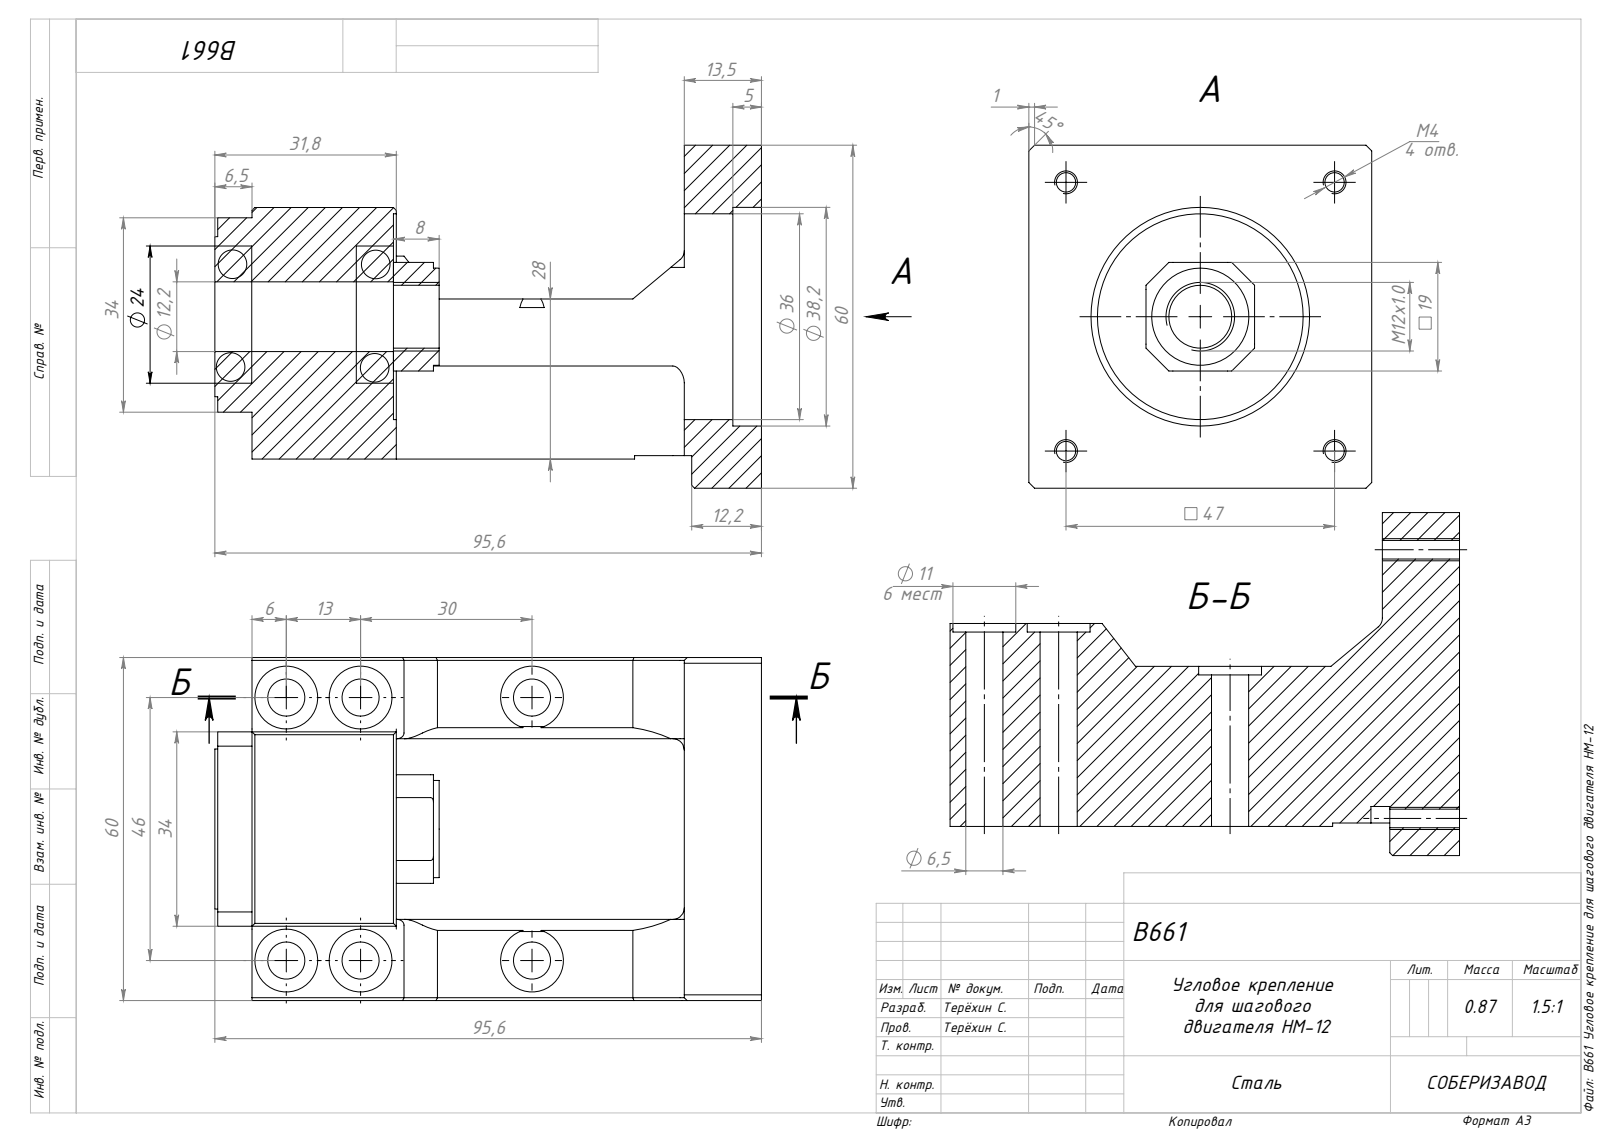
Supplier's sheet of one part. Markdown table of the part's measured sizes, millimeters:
| quantity | value |
| --- | --- |
| part name | B661 Угловое крепление для шагового двигателя HM-12; B661 Угловое крепление для шагового двигателя HM-12_00 |
| STEP written by | SolidWorks 2026 (CONFIG_CONTROL_DESIGN) |
| units | millimeters |
| bodies | 2 solids, 165 faces (89 planar, 74 cylindrical, 2 other) |
| overall size | 95.65 × 60 × 60 |
| volume | 130 514 mm³ |
| surface area | 34 753 mm² |
| round holes (diameter × count) | 11 × 7, 6.5 × 6, 3.4 × 4, 7.6 × 4, 12.2 × 1, 36 × 1, 38.25 × 1 |
| round bosses / shafts (diameter × count) | 28 × 1, 17 × 1 |
| partial cylindrical surfaces (radius × count) | 0.5 × 10, 1 × 4, 2 × 3, 2.15 × 2 |
| main face-to-face distances | 60, 14.2, 45.8, 89.15, 13.5, 75.65, 64.4, 50.9, 24.75, 31.6 |
| hole center spacings | 37.64, 15.56, 17.68, 25, 33.23, 47, 50.91, 46 |
